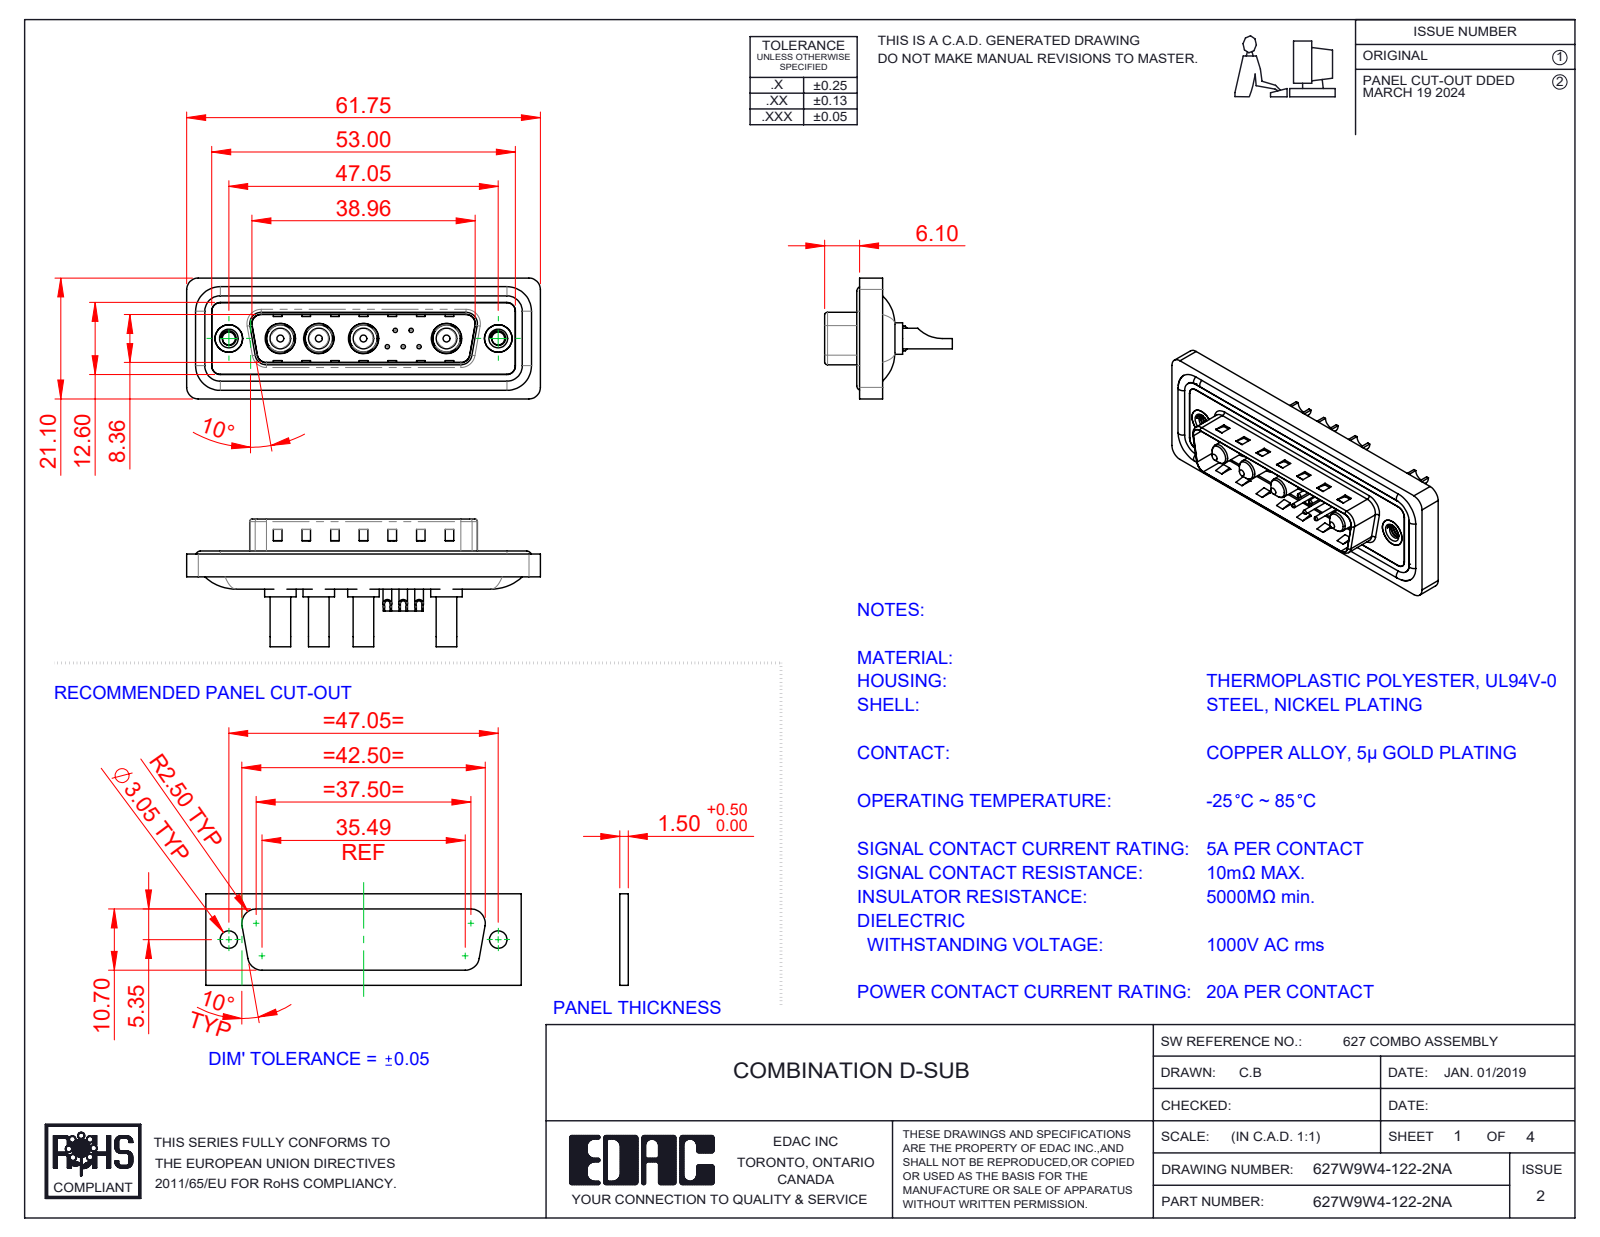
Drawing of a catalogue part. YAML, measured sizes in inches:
part_name: "627W9W4-122-2NA; 627Combo Housing_9W4; Power Pin_20A SC; 627Combo Waterproof Housing_25 Contacts (+5 more)"
step_written_by: "SolidWorks 2023 (CONFIG_CONTROL_DESIGN)"
units: inches
bodies: {solids: 20, faces: 846, planar: 306, cylindrical: 358, other: 182}
overall_size: [2.431, 0.878, 0.831]
volume: 0.456
surface_area: 18.91
round_holes:
  - {diameter: 0.03, count: 5}
  - {diameter: 0.039, count: 5}
  - {diameter: 0.063, count: 5}
  - {diameter: 0.079, count: 5}
  - {diameter: 0.106, count: 4}
  - {diameter: 0.191, count: 4}
  - {diameter: 0.209, count: 4}
  - {diameter: 0.089, count: 2}
  - {diameter: 0.157, count: 2}
  - {diameter: 0.189, count: 2}
  - {diameter: 0.197, count: 2}
round_bosses_or_shafts:
  - {diameter: 0.059, count: 5}
  - {diameter: 0.217, count: 4}
  - {diameter: 0.205, count: 4}
  - {diameter: 0.187, count: 4}
  - {diameter: 0.148, count: 4}
  - {diameter: 0.142, count: 4}
  - {diameter: 0.063, count: 4}
  - {diameter: 0.193, count: 2}
partial_cylinders:
  - {radius: 0.059, count: 22}
  - {radius: 0.079, count: 18}
  - {radius: 0.02, count: 8}
  - {radius: 0.063, count: 8}
  - {radius: 0.039, count: 6}
  - {radius: 0.01, count: 4}
  - {radius: 0.024, count: 4}
  - {radius: 0.026, count: 4}
face_to_face_distances: [0.016, 0.059, 0.043, 0.02, 0.063, 0.122, 0.114, 0.032, 0.377, 0.222]
hole_center_spacings: [0.124, 0.109, 0.198, 0.571, 0.109, 0.173, 0.174, 0.197]
